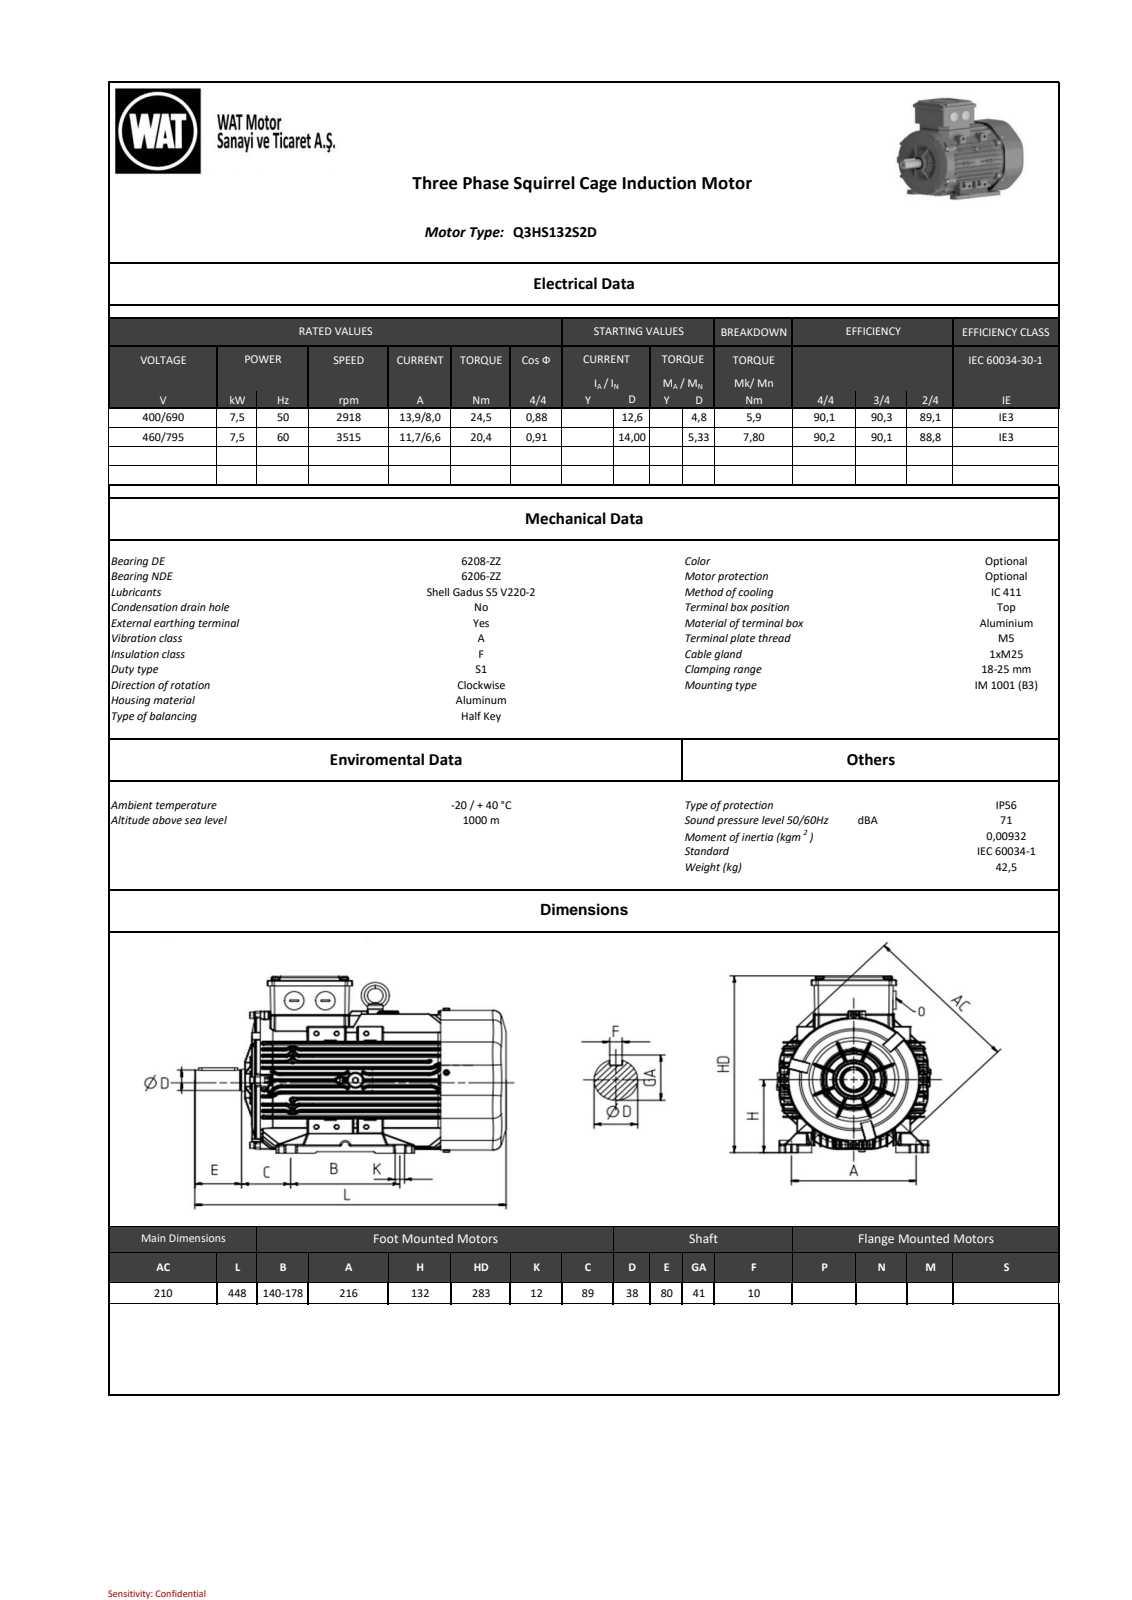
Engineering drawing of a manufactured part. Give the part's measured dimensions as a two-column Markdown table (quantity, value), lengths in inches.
| quantity | value |
| --- | --- |
| part name | Ar311510F80553gq |
| STEP written by | SIEMENS PLM Software NX 9.0 (AUTOMOTIVE_DESIGN) |
| units | inches |
| bodies | 0 solids, 11206 faces (2365 planar, 3389 cylindrical, 5452 other) |
| overall size | 17.614 × 11.141 × 9.633 |
| round holes (diameter × count) | 0.327 × 4, 0.262 × 3, 0.472 × 2, 1.094 × 2, 0.138 × 1, 0.157 × 1, 0.186 × 1, 0.194 × 1, 0.256 × 1, 0.315 × 1, 0.406 × 1, 0.512 × 1 |
| round bosses / shafts (diameter × count) | 0.315 × 12, 0.583 × 4, 0.512 × 4, 0.465 × 4, 0.394 × 4, 0.236 × 4, 7.402 × 1, 2.402 × 1 |
| partial cylindrical surfaces (radius × count) | 0.02 × 808, 0.039 × 581, 0.031 × 530, 0.079 × 236, 0.118 × 43, 0.012 × 20, 0.197 × 12, 0.394 × 9 |
| main face-to-face distances | 9.567, 0.039, 0.197, 0.846, 1.416, 0.433, 3.919, 0.983, 4.444, 0.321 |
| hole center spacings | 1.575, 4.331, 2.859, 4.867, 5.669, 7.134, 3.796, 3.799 |
